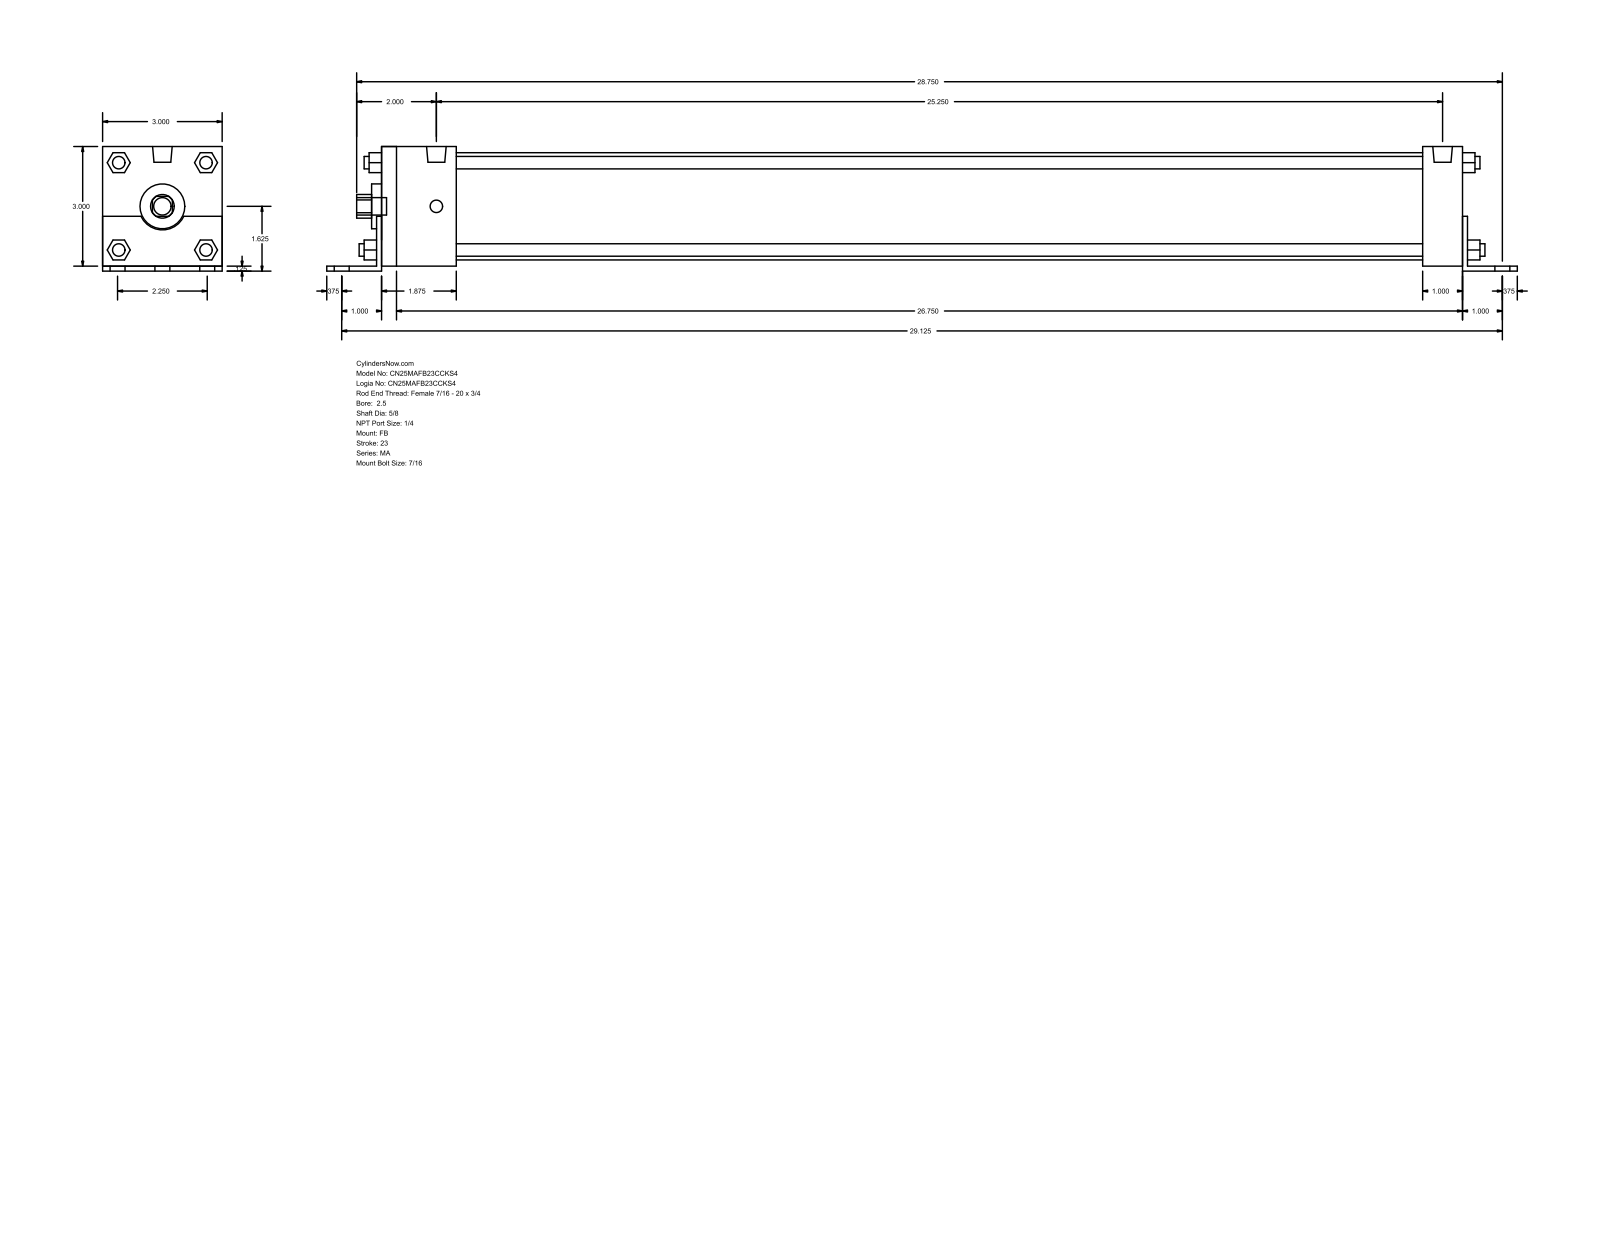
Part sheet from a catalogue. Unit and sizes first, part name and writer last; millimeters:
Units: millimetres
Overall size (bounding box): 758.83 × 79.38 × 76.2
Round holes (diameter × count): ⌀15.88 ×1, ⌀28.57 ×1, ⌀68.33 ×1
Round bosses / shafts (diameter × count): ⌀7.94 ×8, ⌀11.11 ×7, ⌀12.49 ×2
Partial cylindrical surfaces — rounded edges, fillets, slot ends (radius × count): R7.54 ×1, R15.05 ×1
Main face-to-face distances: 76.2, 3.17, 79.37, 688.97, 695.32, 3.18, 692.14, 47.62, 25.4, 692.15
Bodies: 0 solids, 140 faces (105 planar, 35 cylindrical, 0 other)
Part name (STEP PRODUCT): MA_FB__0250_0.625
STEP written by: GSSL Pune (CONFIG_CONTROL_DESIGN)
